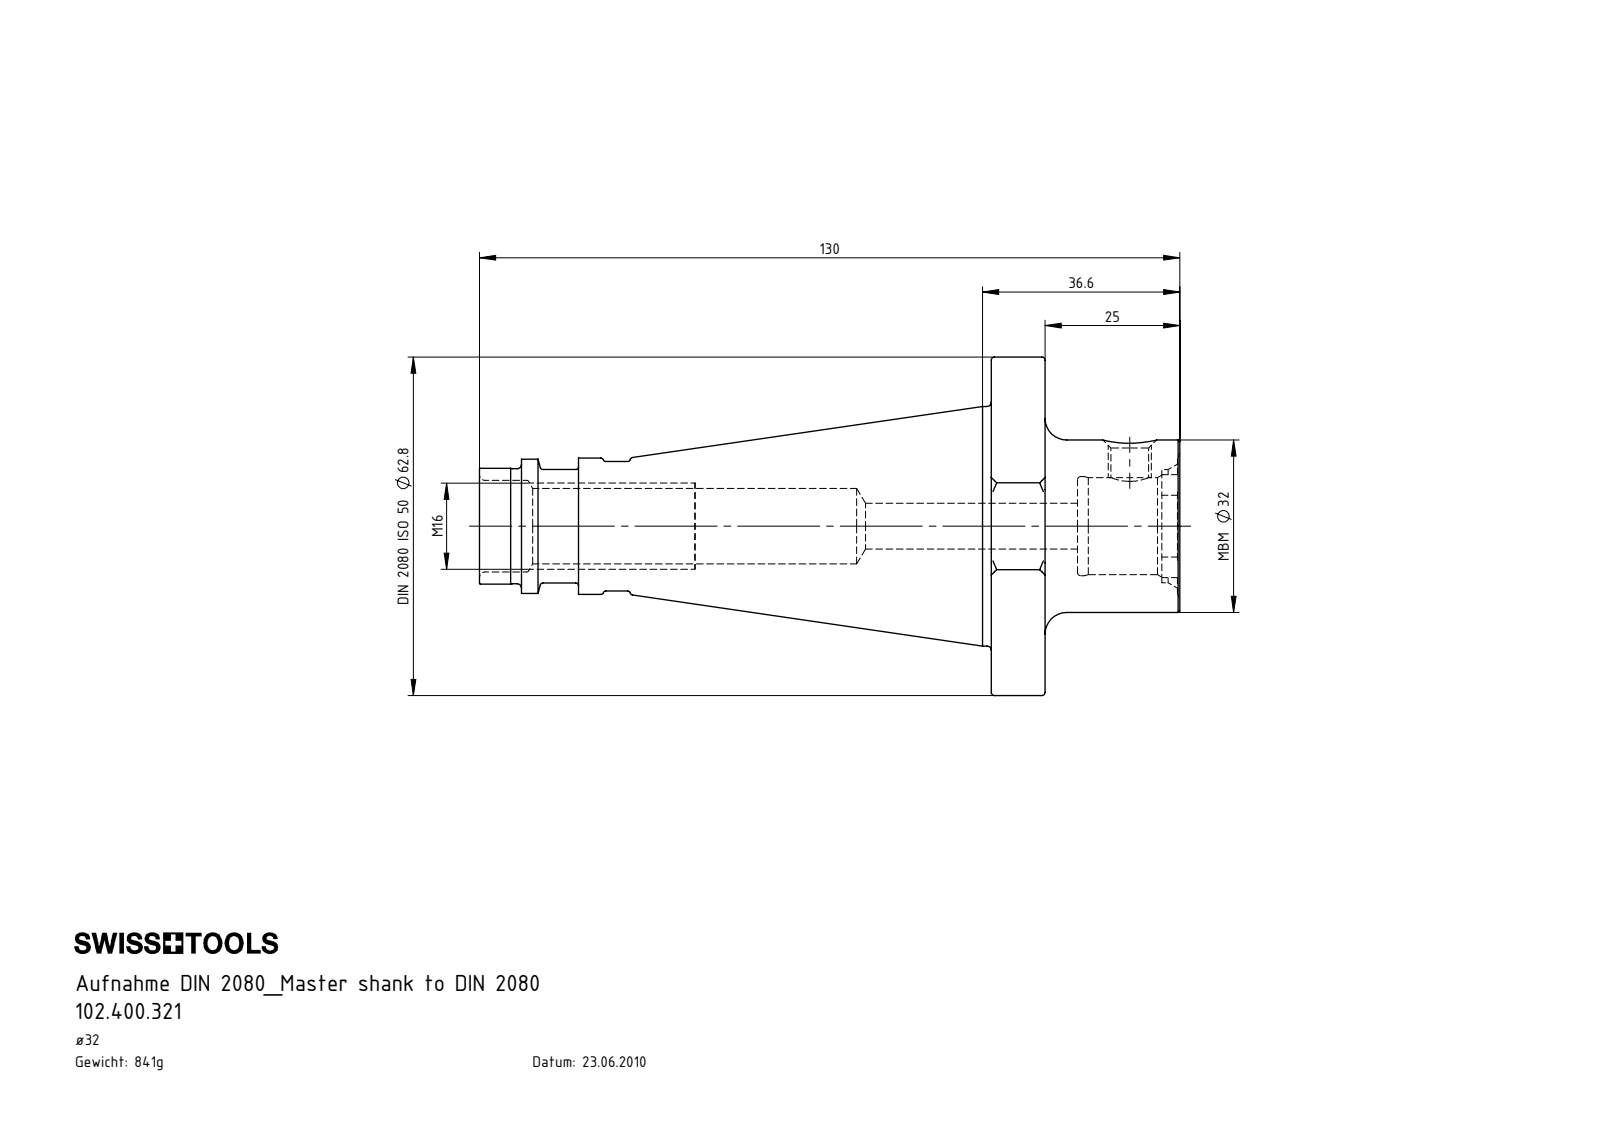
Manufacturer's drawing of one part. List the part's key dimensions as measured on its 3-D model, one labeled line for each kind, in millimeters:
Part name (STEP PRODUCT): 102.400.321
STEP written by: SolidWorks 2017 (CONFIG_CONTROL_DESIGN)
Units: millimetres
Bodies: 1 solid, 140 faces (33 planar, 53 cylindrical, 54 other)
Overall size (bounding box): 130 × 62.8 × 60.7
Volume: 107 191 mm³ · Surface area: 23 977 mm²
Round holes (diameter × count): ⌀7 ×1, ⌀8.5 ×1, ⌀14 ×1, ⌀17 ×1, ⌀18 ×1, ⌀18.4 ×1
Round bosses / shafts (diameter × count): ⌀62.8 ×1, ⌀44.45 ×1, ⌀32 ×1, ⌀25.3 ×1, ⌀24.91 ×1, ⌀24 ×1, ⌀21.5 ×1, ⌀21.35 ×1
Partial cylindrical surfaces — rounded edges, fillets, slot ends (radius × count): R1.6 ×12, R3.2 ×4, R10.5 ×1, R12.18 ×1
Main face-to-face distances: 10, 35, 25, 16, 6, 19, 31.65, 21.65, 15.65, 3.35
